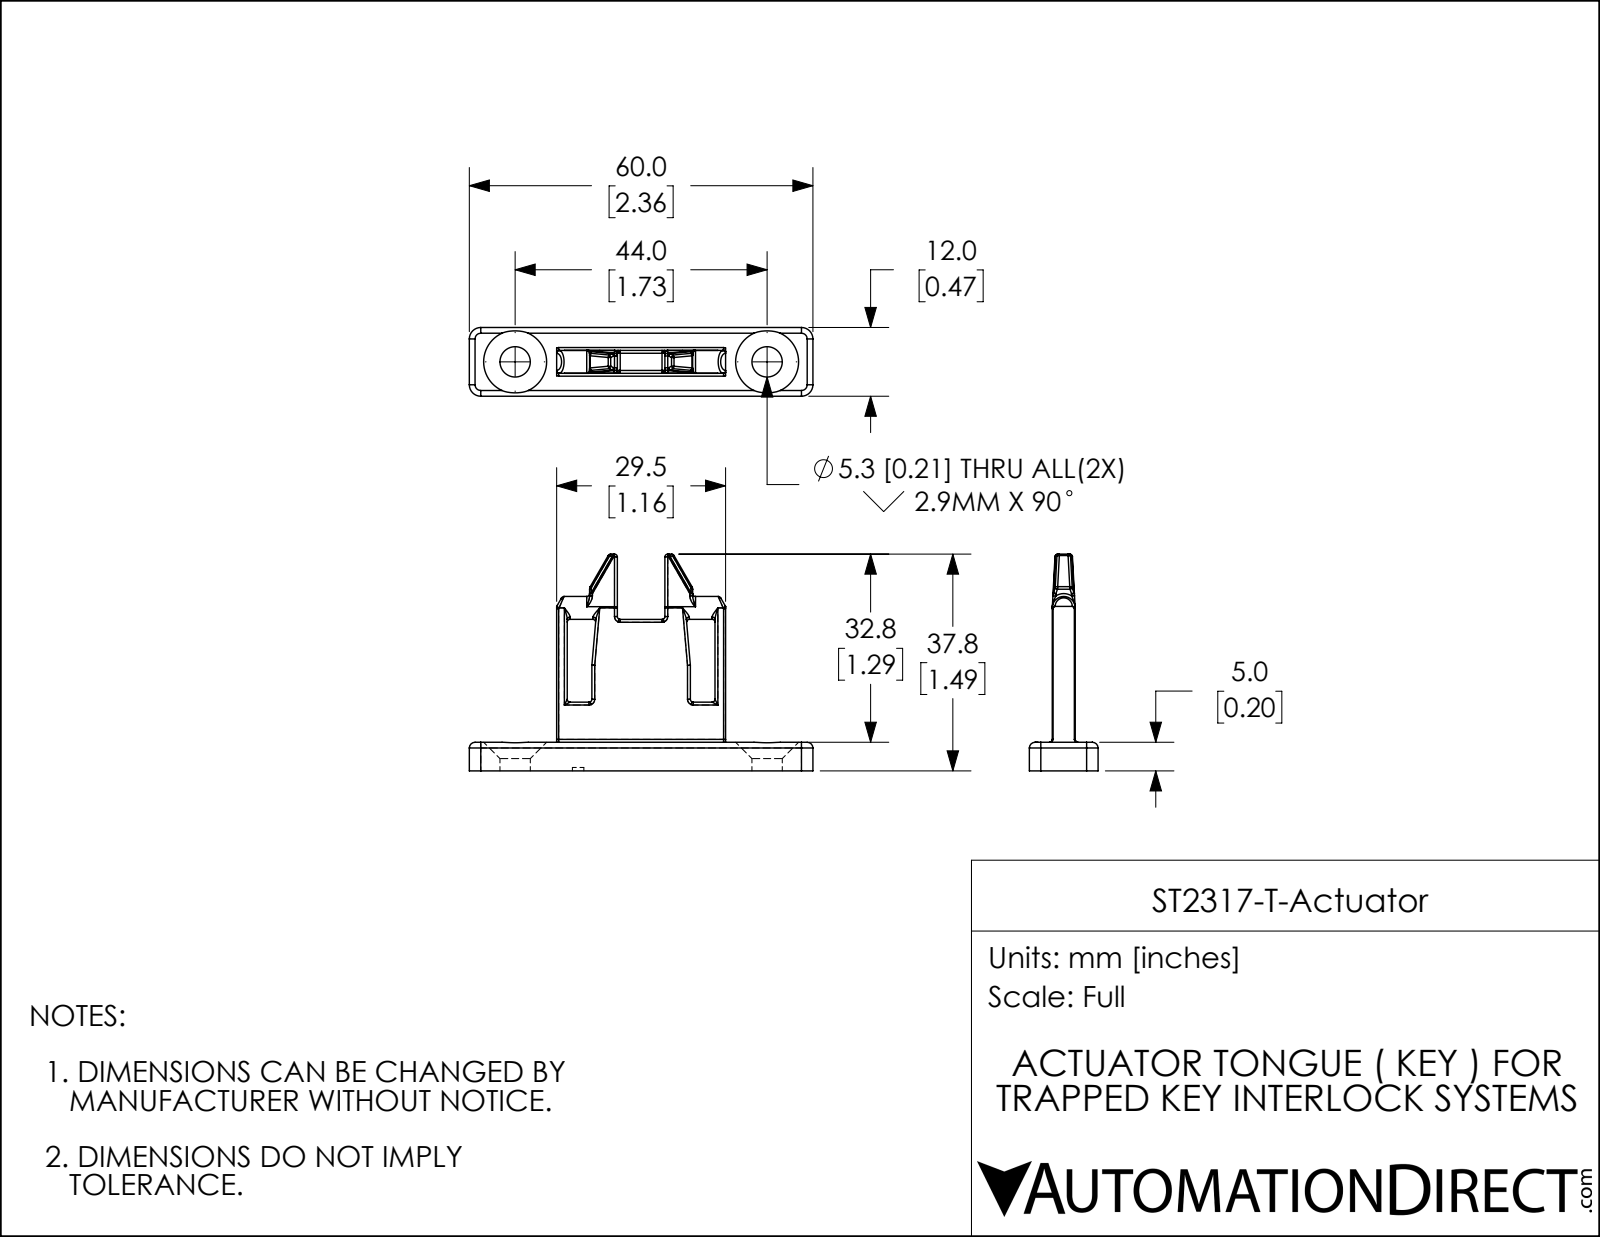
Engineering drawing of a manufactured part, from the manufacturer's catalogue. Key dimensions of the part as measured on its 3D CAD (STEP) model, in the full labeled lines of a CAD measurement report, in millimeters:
Part name (STEP PRODUCT): ST2317-T-Actuator
STEP written by: SolidWorks 2018 (AUTOMOTIVE_DESIGN)
Units: millimetres
Bodies: 1 solid, 206 faces (40 planar, 86 cylindrical, 80 other)
Overall size (bounding box): 60 × 37.8 × 12
Volume: 5 620 mm³ · Surface area: 3 890 mm²
Round holes (diameter × count): ⌀5.3 ×2, ⌀2 ×1
Round bosses / shafts (diameter × count): ⌀4 ×1
Partial cylindrical surfaces — rounded edges, fillets, slot ends (radius × count): R0.5 ×67, R1 ×4, R2 ×4, R0.9 ×2
Main face-to-face distances: 4, 8, 5, 12, 29.5, 1.9, 27.7, 15.2, 17.1, 42.9
Hole centre spacings: 11, 33, 44
